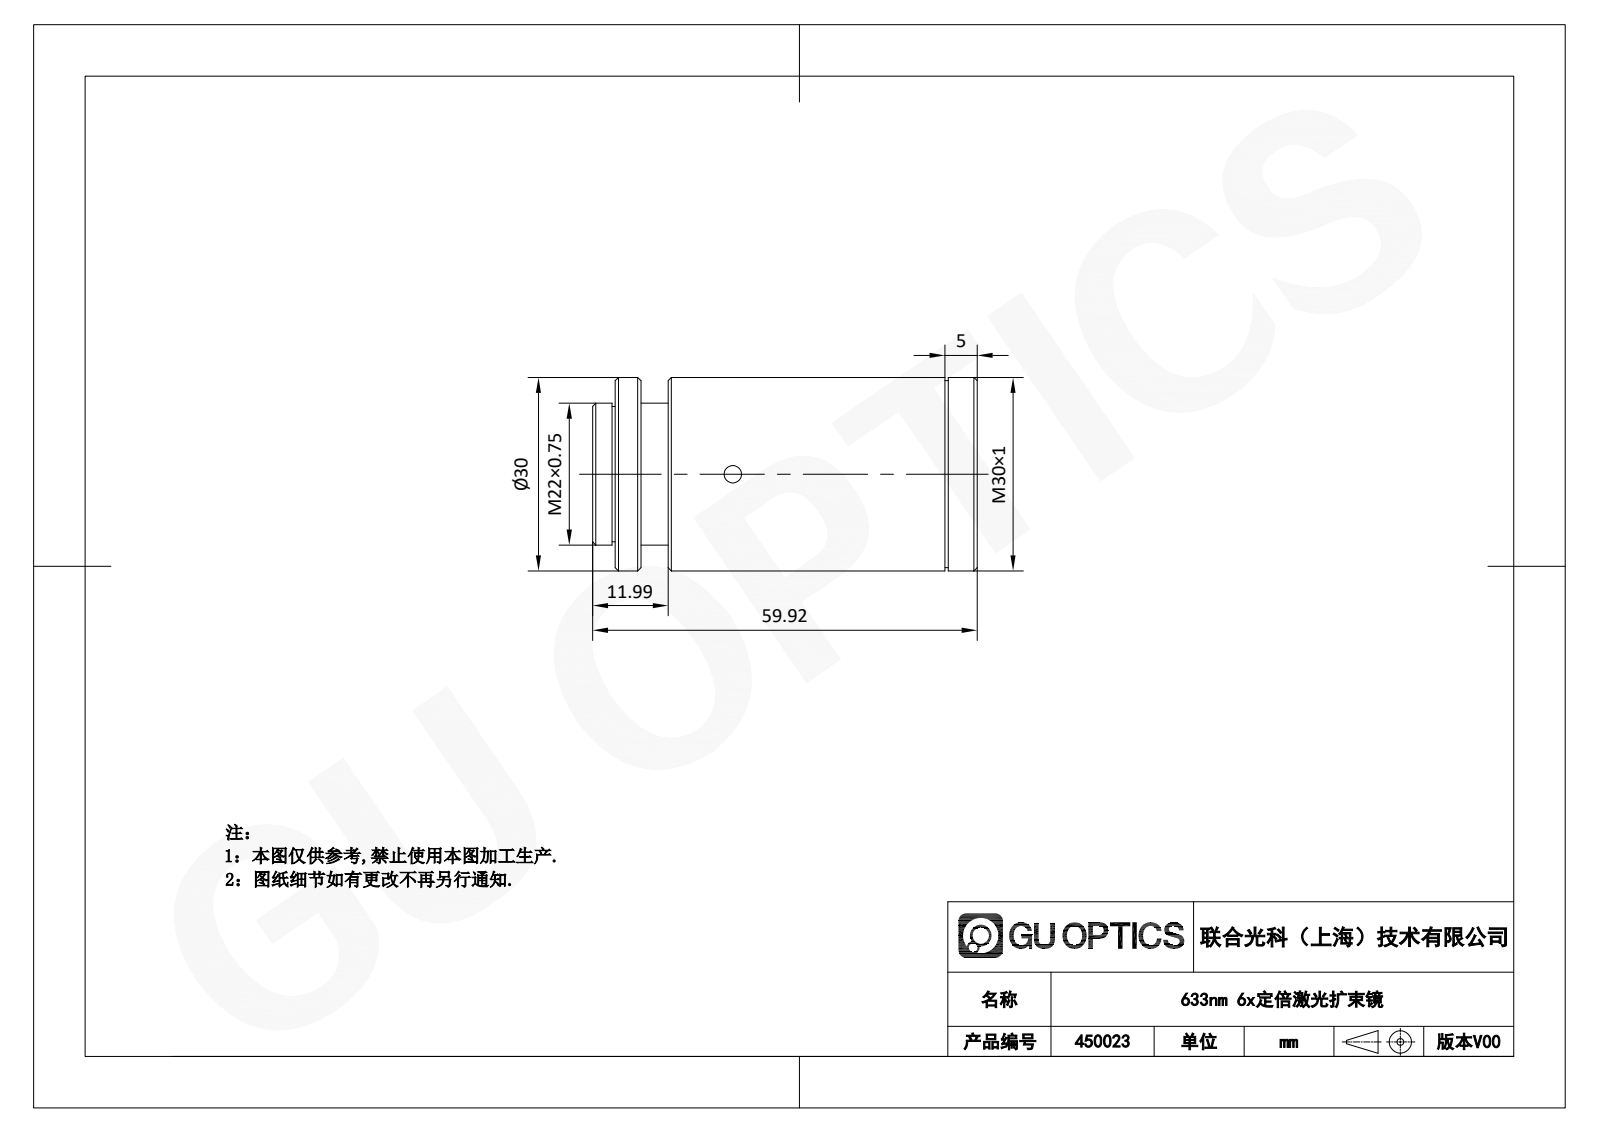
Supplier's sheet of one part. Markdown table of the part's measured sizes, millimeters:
| quantity | value |
| --- | --- |
| part name | 450023 |
| STEP written by | SolidWorks 2020 (CONFIG_CONTROL_DESIGN) |
| units | millimeters |
| bodies | 1 solid, 44 faces (12 planar, 22 cylindrical, 10 other) |
| overall size | 59.92 × 30 × 30 |
| volume | 38 729 mm³ |
| surface area | 8 361 mm² |
| round holes (diameter × count) | 2 × 1, 8 × 1, 18 × 1, 20 × 1 |
| round bosses / shafts (diameter × count) | 30 × 1, 29 × 1, 22 × 1, 21 × 1 |
| main face-to-face distances | 2, 57.92, 1, 56.42, 52.42, 1.5, 2.5, 54.42, 3.5, 59.92 |
